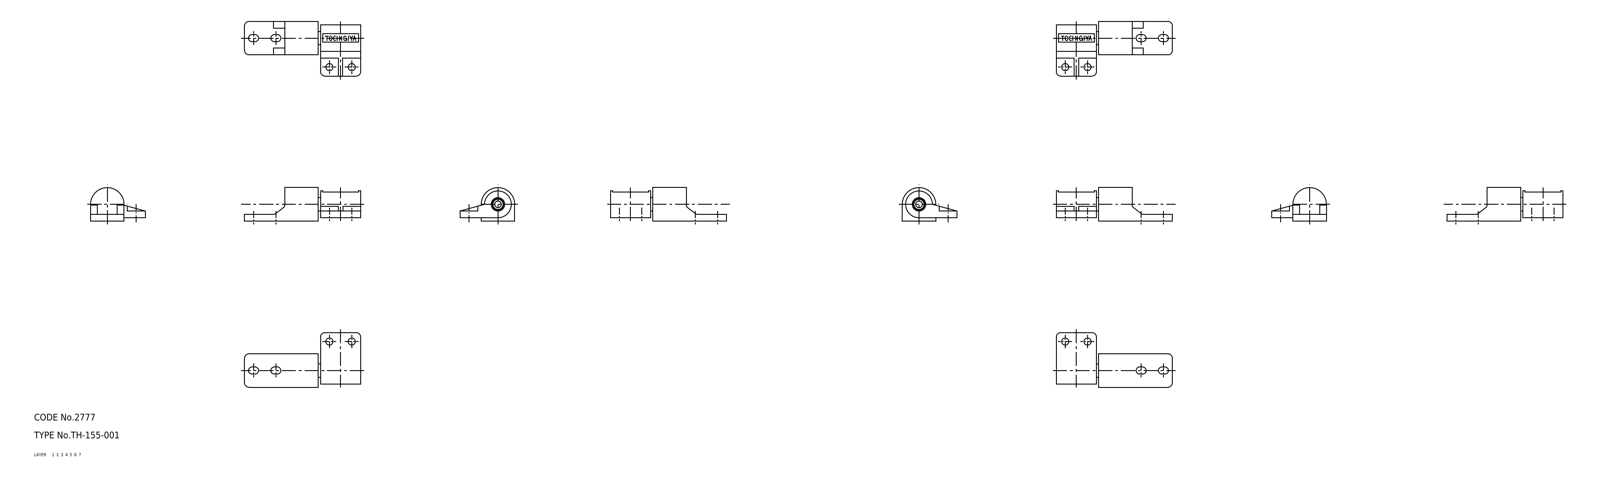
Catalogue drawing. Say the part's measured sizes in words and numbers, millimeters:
The part is named "67113925; 67113938; 67113951; 67113964". Its 3-D file was written by "CADfix (AUTOMOTIVE_DESIGN)". It is 4 solids with 112 faces: 0 planar, 0 cylindrical and 112 other. Overall it measures 165.62 by 24.5 by 15 millimeters. Its volume is 13 272 cubic millimeters and its surface area 6 850 square millimeters.
